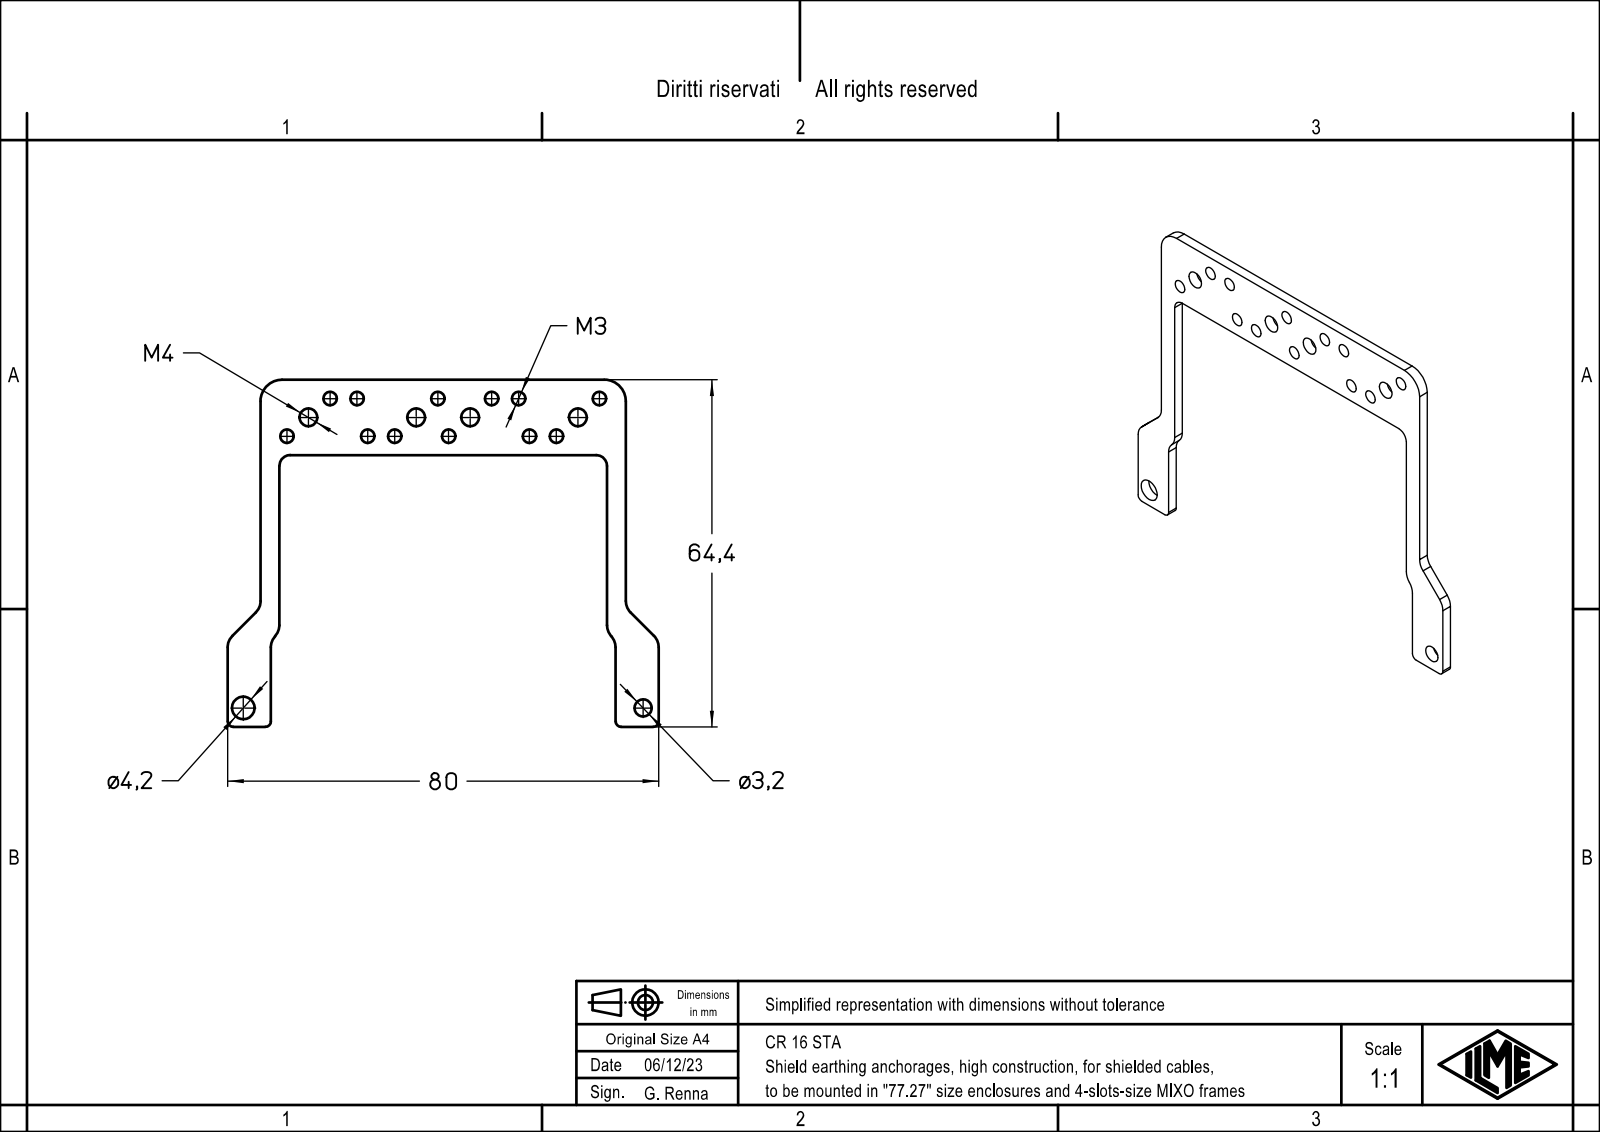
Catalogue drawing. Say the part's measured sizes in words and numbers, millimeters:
The part is named "CR_16_STA". Its 3-D file was written by "Creo Elements/Direct Modeling 20.5B 27-May-2023 (C) Parametric Technology GmbH (AUTOMOTIVE_DESIGN)". It is 1 solid with 68 faces: 16 planar, 52 cylindrical and 0 other. Overall it measures 80 by 64.4 by 2 millimeters. Its volume is 2 719 cubic millimeters and its surface area 3 783 square millimeters. Round holes: 12 of diameter 2.5, 4 of diameter 3.3, 1 of diameter 3.2, 1 of diameter 4.2. Partial cylindrical surfaces (rounded edges, fillets, slot ends): 8 of radius 3, 4 of radius 1, 2 of radius 2, 2 of radius 4. The main face-to-face distances are 2, 3.5, 64.3, 14, 67.8, 60.8, 1.9, 65.9, 1.6, 62.4. The hole center spacings are 5.32, 30, 15, 20, 5, 9.66, 9.9, 10.63.
